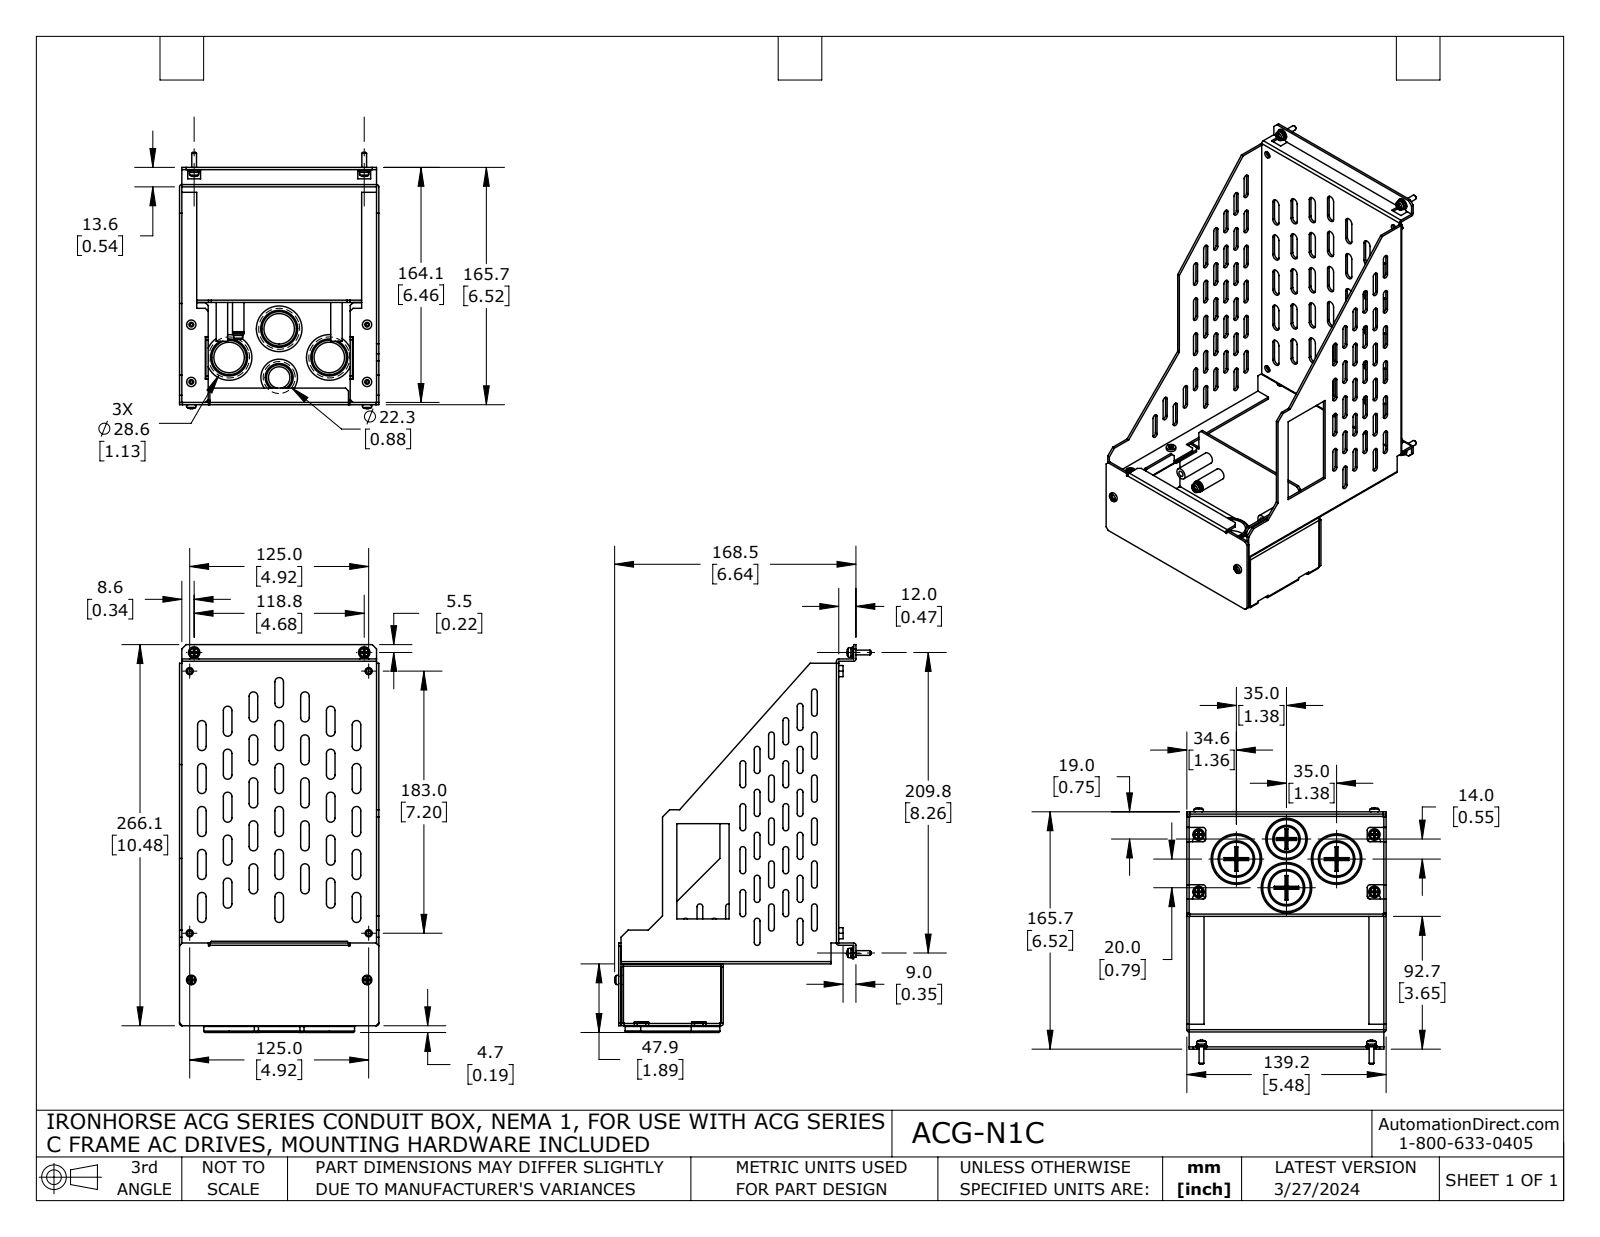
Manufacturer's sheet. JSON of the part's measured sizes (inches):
{"part_name": "ACG-N1C", "step_written_by": "SolidWorks 2021 (AUTOMOTIVE_DESIGN)", "units": "inches", "bodies": {"solids": 18, "faces": 1452, "planar": 742, "cylindrical": 571, "other": 139}, "overall_size": [10.661, 7.049, 5.48], "volume_in3": 10.92, "surface_area_in2": 359.9, "round_holes": [[0.13, 10], [0.197, 4], [0.335, 4], [0.157, 3], [0.925, 3], [1.126, 3], [1.272, 3], [0.169, 2], [0.677, 1], [0.878, 1], [1.024, 1]], "round_bosses_or_shafts": [[0.315, 11], [0.259, 9], [0.256, 6], [0.13, 5], [1.39, 3], [1.256, 3], [1.098, 3], [1.142, 1]], "partial_cylinders_radius": [[0.079, 78], [0.118, 72], [0.02, 26], [0.063, 17], [0.089, 4], [0.098, 4], [0.197, 2]], "face_to_face_distances": [0.063, 5.417, 5.988, 5.48, 5.354, 3.177, 2.811, 5.925, 1.701, 2.748], "hole_center_spacings": [4.835, 0.197, 1.575, 4.839, 5.085, 0.9, 1.143, 1.238]}
